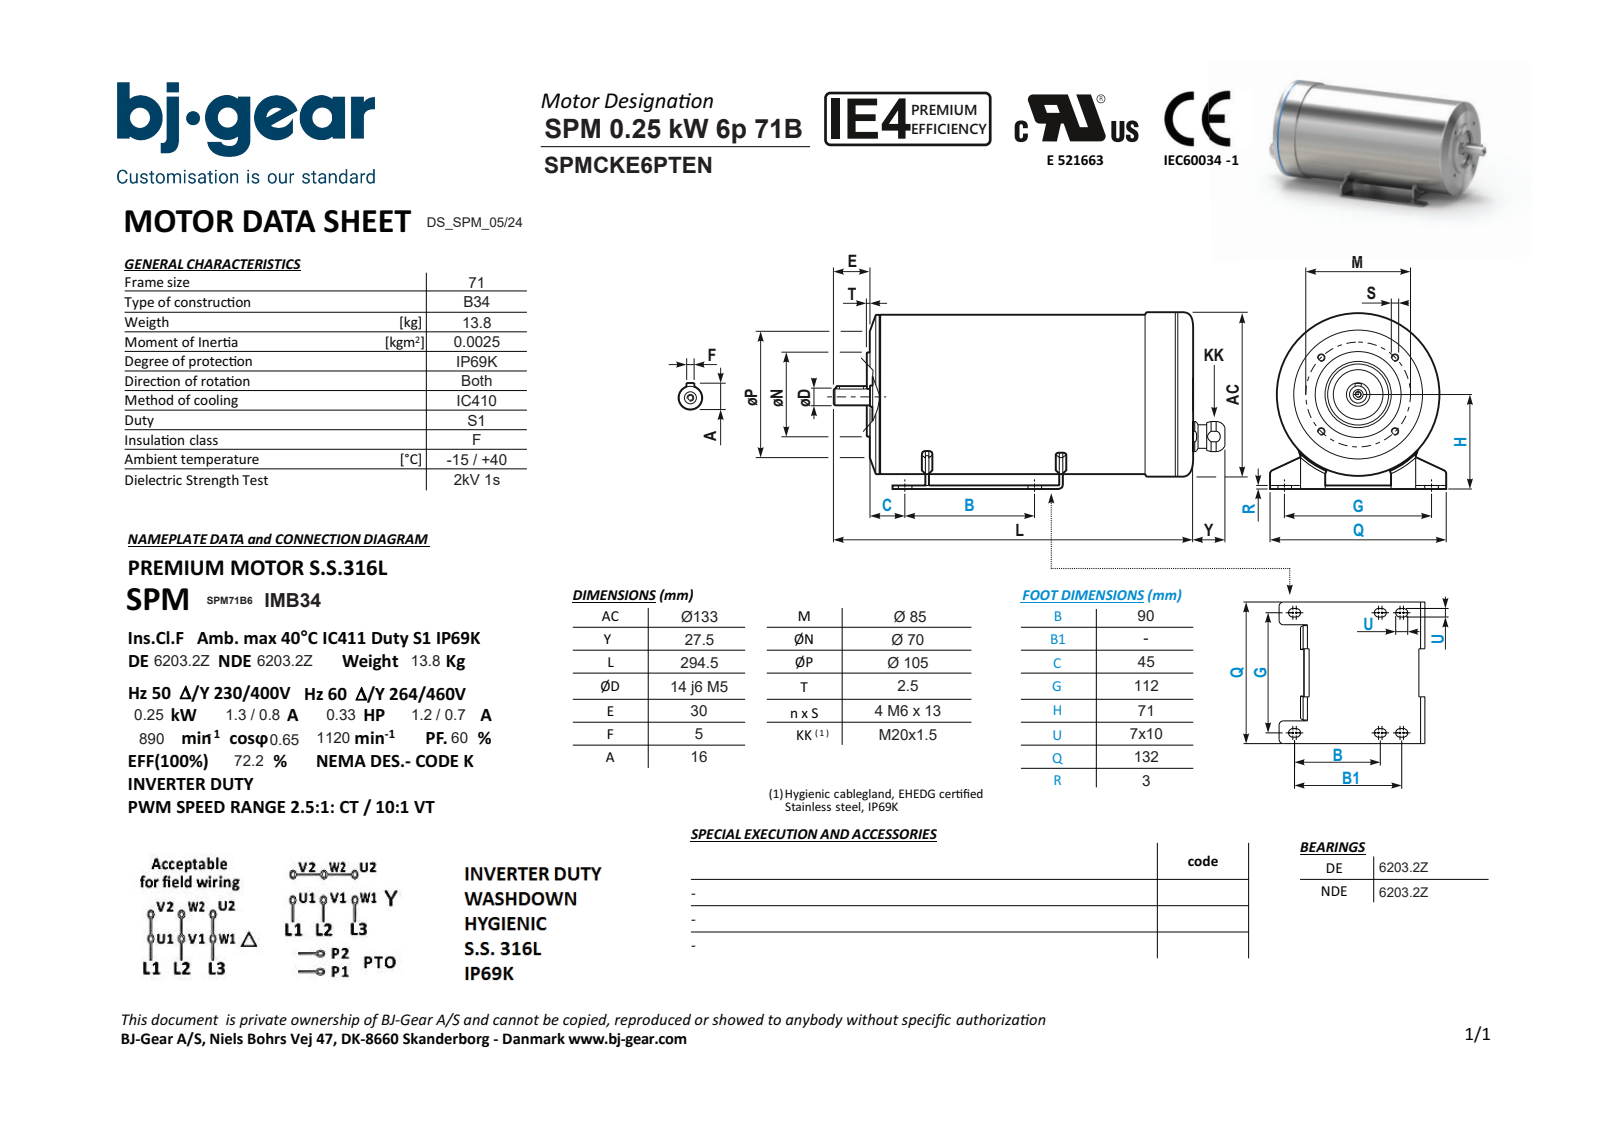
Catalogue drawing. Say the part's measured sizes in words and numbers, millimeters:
The part is named "SPMCKF2PTENN4KSA1-N---NNN; SPMCKF2JTENN4KSA1-N---NNN; SPM719022". Its 3-D file was written by "Solid Edge (AUTOMOTIVE_DESIGN)". It is 2 solids with 160 faces: 67 planar, 67 cylindrical and 26 other. Overall it measures 322 by 137.5 by 133 millimeters. Its volume is 3 515 000 cubic millimeters and its surface area 170 633 square millimeters. Round holes: 4 of diameter 4.92, 1 of diameter 4.13, 1 of diameter 5.3, 1 of diameter 7, 1 of diameter 13.4, 1 of diameter 52, 1 of diameter 62, 1 of diameter 129. Round bosses or shafts: 1 of diameter 133, 1 of diameter 132.98, 1 of diameter 128.98, 1 of diameter 70, 1 of diameter 20, 1 of diameter 17, 1 of diameter 14. Partial cylindrical surfaces (rounded edges, fillets, slot ends): 8 of radius 3, 8 of radius 3.5, 4 of radius 1, 4 of radius 5, 2 of radius 2.5, 2 of radius 4, 1 of radius 12.8. The main face-to-face distances are 3, 264.5, 259, 5.5, 107.5, 110.5, 151.5, 157, 148.5, 154. The hole center spacings are 42.5, 60.1, 30.31, 70.75, 84.99, 34.
